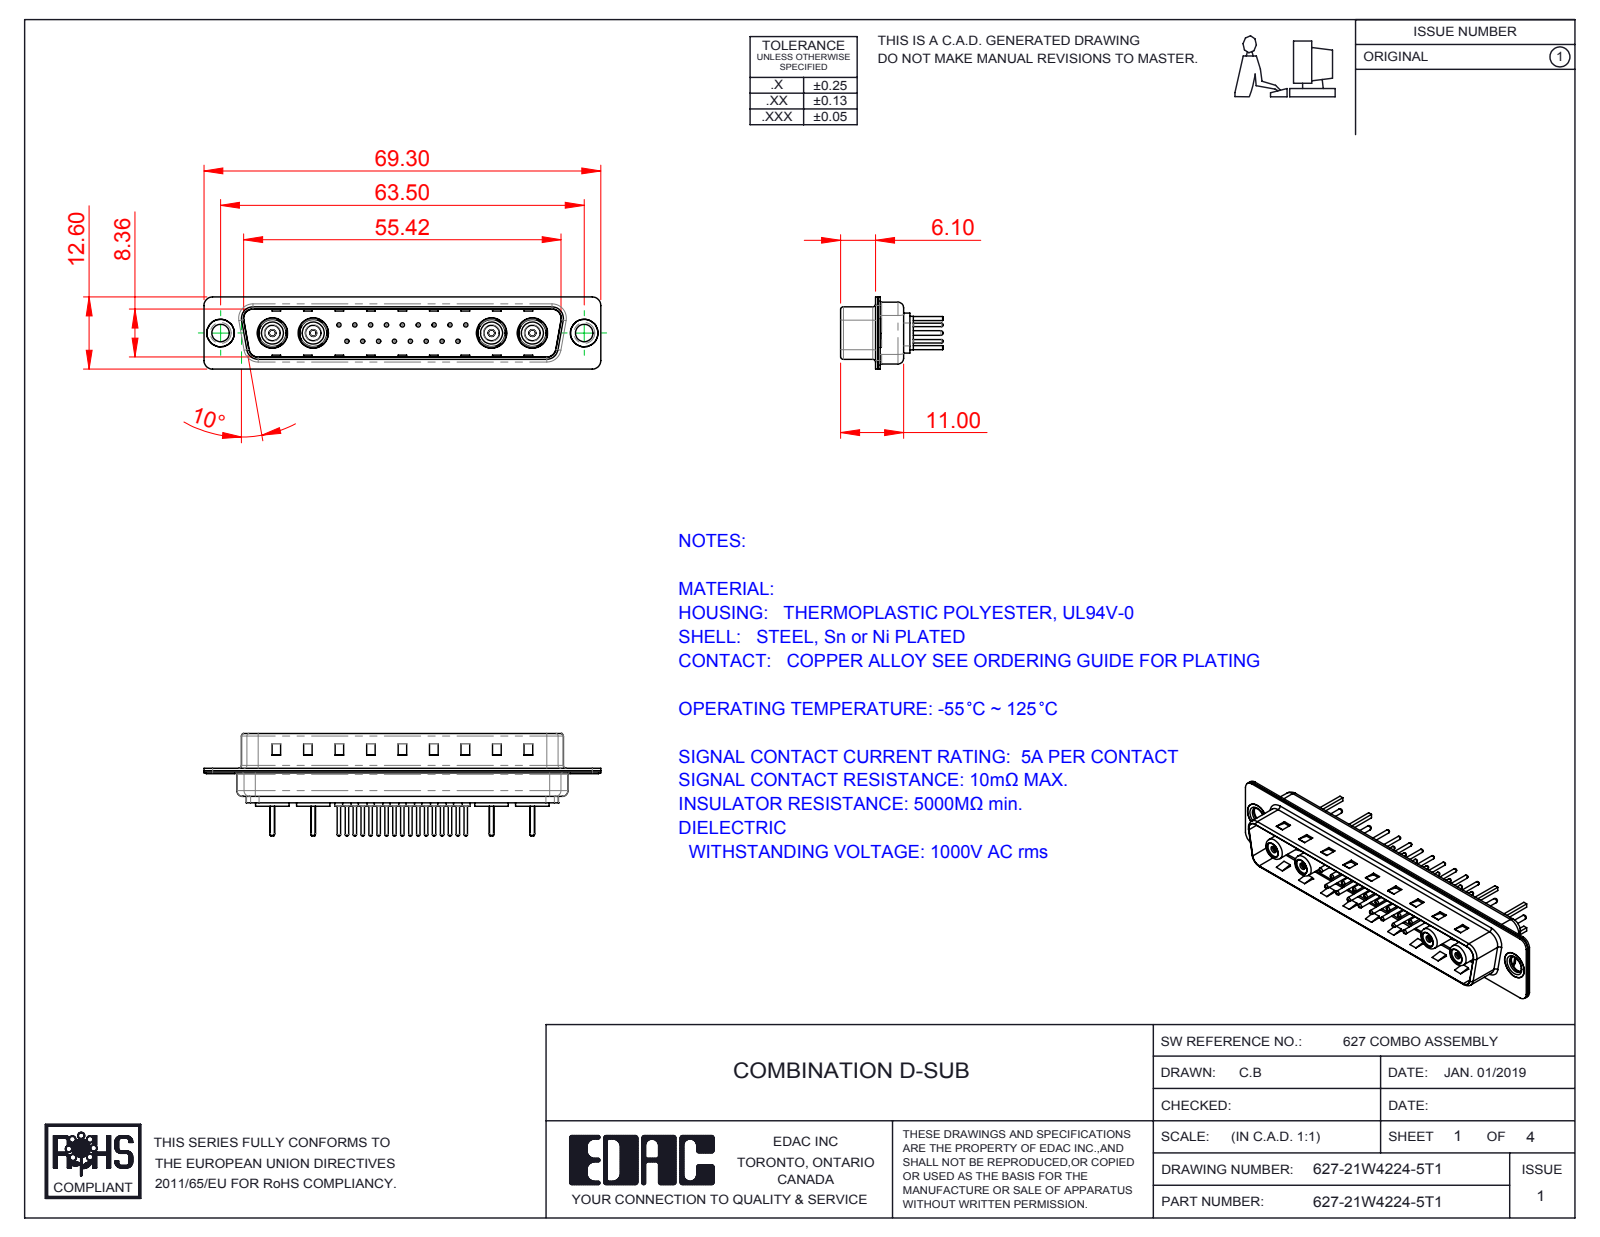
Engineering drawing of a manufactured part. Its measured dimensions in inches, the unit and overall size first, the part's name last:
Units: inches
Overall size (bounding box): 2.728 × 0.705 × 0.496
Round holes (diameter × count): ⌀0.063 ×21, ⌀0.03 ×17, ⌀0.079 ×17, ⌀0.043 ×4, ⌀0.047 ×4, ⌀0.059 ×4, ⌀0.098 ×4, ⌀0.106 ×4, ⌀0.134 ×4, ⌀0.191 ×4, ⌀0.209 ×4, ⌀0.12 ×2
Round bosses / shafts (diameter × count): ⌀0.059 ×17, ⌀0.024 ×17, ⌀0.23 ×4, ⌀0.205 ×4, ⌀0.189 ×4, ⌀0.186 ×4, ⌀0.152 ×4, ⌀0.148 ×4
Partial cylindrical surfaces — rounded edges, fillets, slot ends (radius × count): R0.059 ×16, R0.079 ×12, R0.02 ×8, R0.063 ×8, R0.01 ×4, R0.024 ×4, R0.026 ×4, R0.035 ×4
Main face-to-face distances: 0.016, 0.032, 0.377, 0.345, 0.236, 0.22, 0.048, 0.393, 0.017, 0.361
Hole centre spacings: 0.124, 0.109, 0.218, 0.327, 0.198, 0.198, 0.295, 0.398
Volume: 0.23 in³ · Surface area: 16.45 in²
Bodies: 42 solids, 1459 faces (510 planar, 551 cylindrical, 398 other)
Part name (STEP PRODUCT): Co-Ax Jack Assy_S; Locking Collar; 627-21W4224-5T1; Insulator Socket (+8 more)
STEP written by: SolidWorks 2016 (CONFIG_CONTROL_DESIGN)
